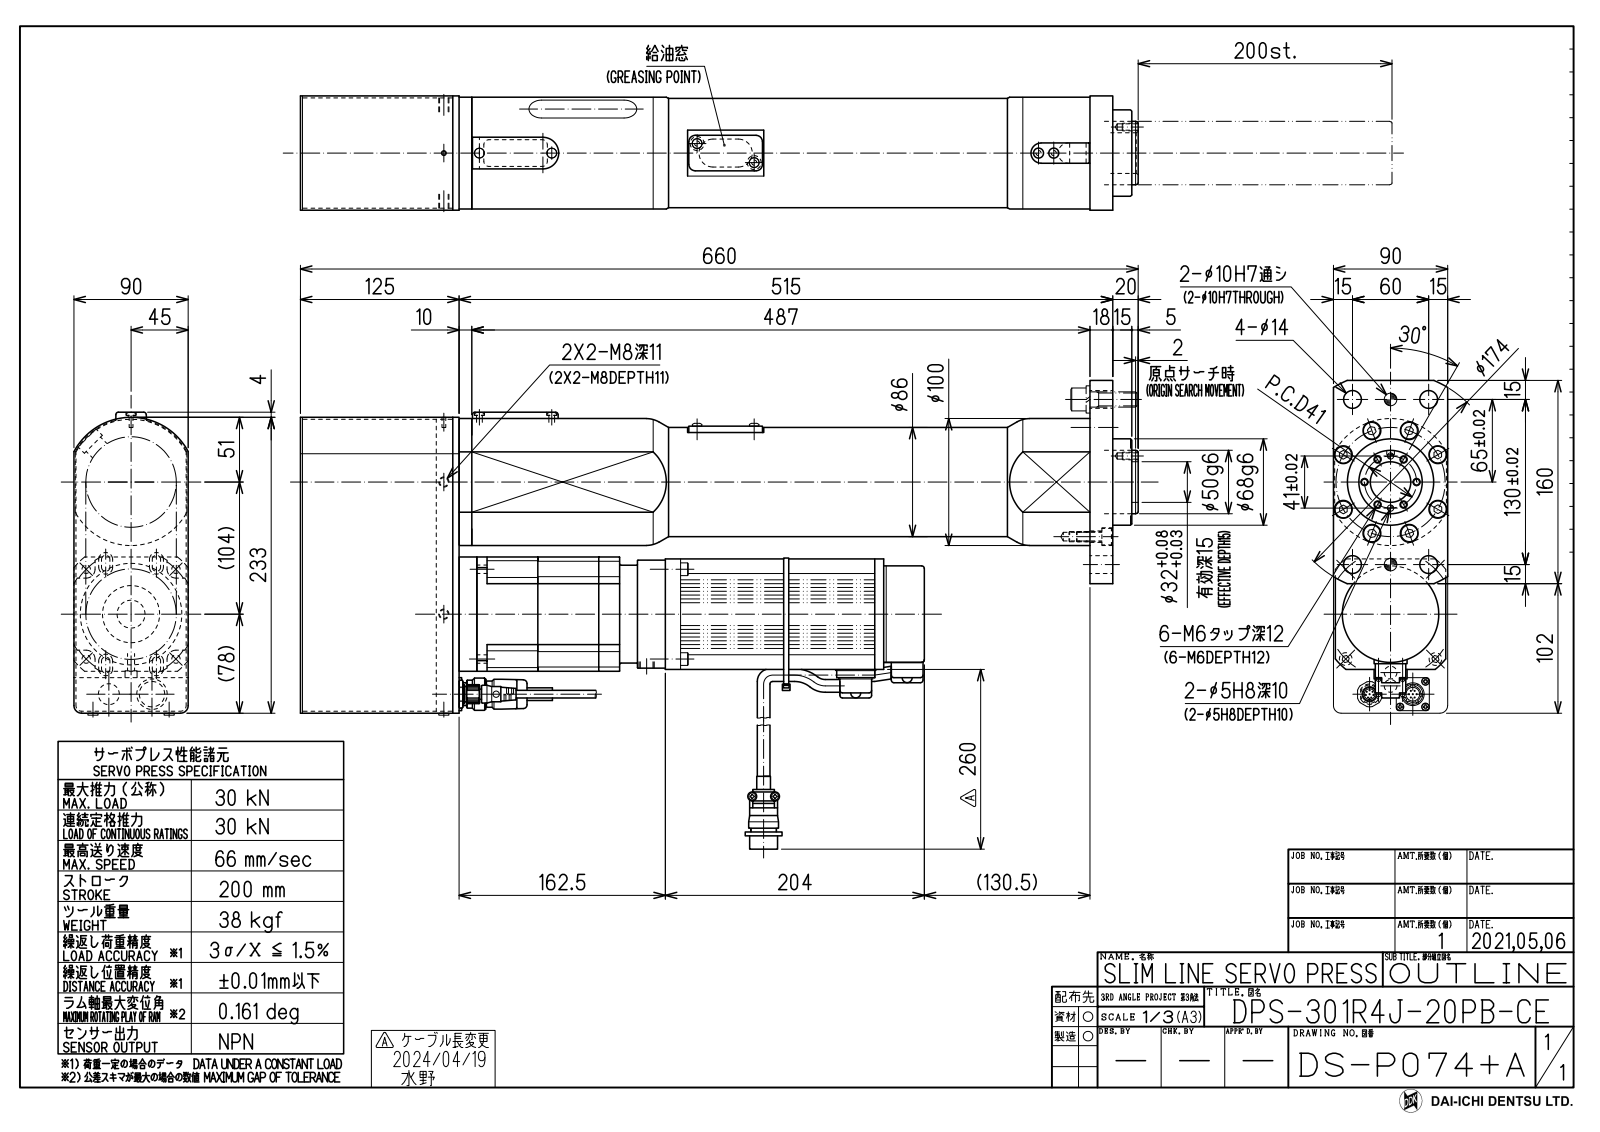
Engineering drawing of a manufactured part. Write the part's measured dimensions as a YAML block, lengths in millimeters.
part_name: "DPS-301R4J-20FB-CE_(DS-P070)_OUTLINE_20220914"
step_written_by: "Autodesk Inventor 2021 (AUTOMOTIVE_DESIGN)"
units: millimeters
bodies: {solids: 1, faces: 1707, planar: 980, cylindrical: 490, other: 237}
overall_size: [660, 263.5, 90]
volume: 8480000
surface_area: 525754
round_holes:
  - {diameter: 4.92, count: 14}
  - {diameter: 14, count: 12}
  - {diameter: 9, count: 8}
  - {diameter: 0.7, count: 4}
  - {diameter: 6.65, count: 4}
  - {diameter: 8, count: 4}
  - {diameter: 5, count: 3}
  - {diameter: 4.5, count: 2}
  - {diameter: 10, count: 2}
  - {diameter: 11, count: 2}
  - {diameter: 16, count: 2}
  - {diameter: 2.46, count: 1}
round_bosses_or_shafts:
  - {diameter: 8, count: 16}
  - {diameter: 13, count: 8}
  - {diameter: 7, count: 6}
  - {diameter: 3, count: 6}
  - {diameter: 10, count: 4}
  - {diameter: 8.5, count: 4}
  - {diameter: 7.5, count: 4}
  - {diameter: 4, count: 4}
partial_cylinders:
  - {radius: 0.6, count: 48}
  - {radius: 1, count: 26}
  - {radius: 2, count: 16}
  - {radius: 0.3, count: 12}
  - {radius: 3, count: 11}
  - {radius: 4.5, count: 10}
  - {radius: 5, count: 10}
  - {radius: 1.5, count: 8}
face_to_face_distances: [1.5, 90, 88.5, 1, 3, 89, 4.5, 7.5, 6, 87.5]
hole_center_spacings: [20.5, 43, 27.25, 61.61, 80.82, 10.61, 23.09, 24.75]
